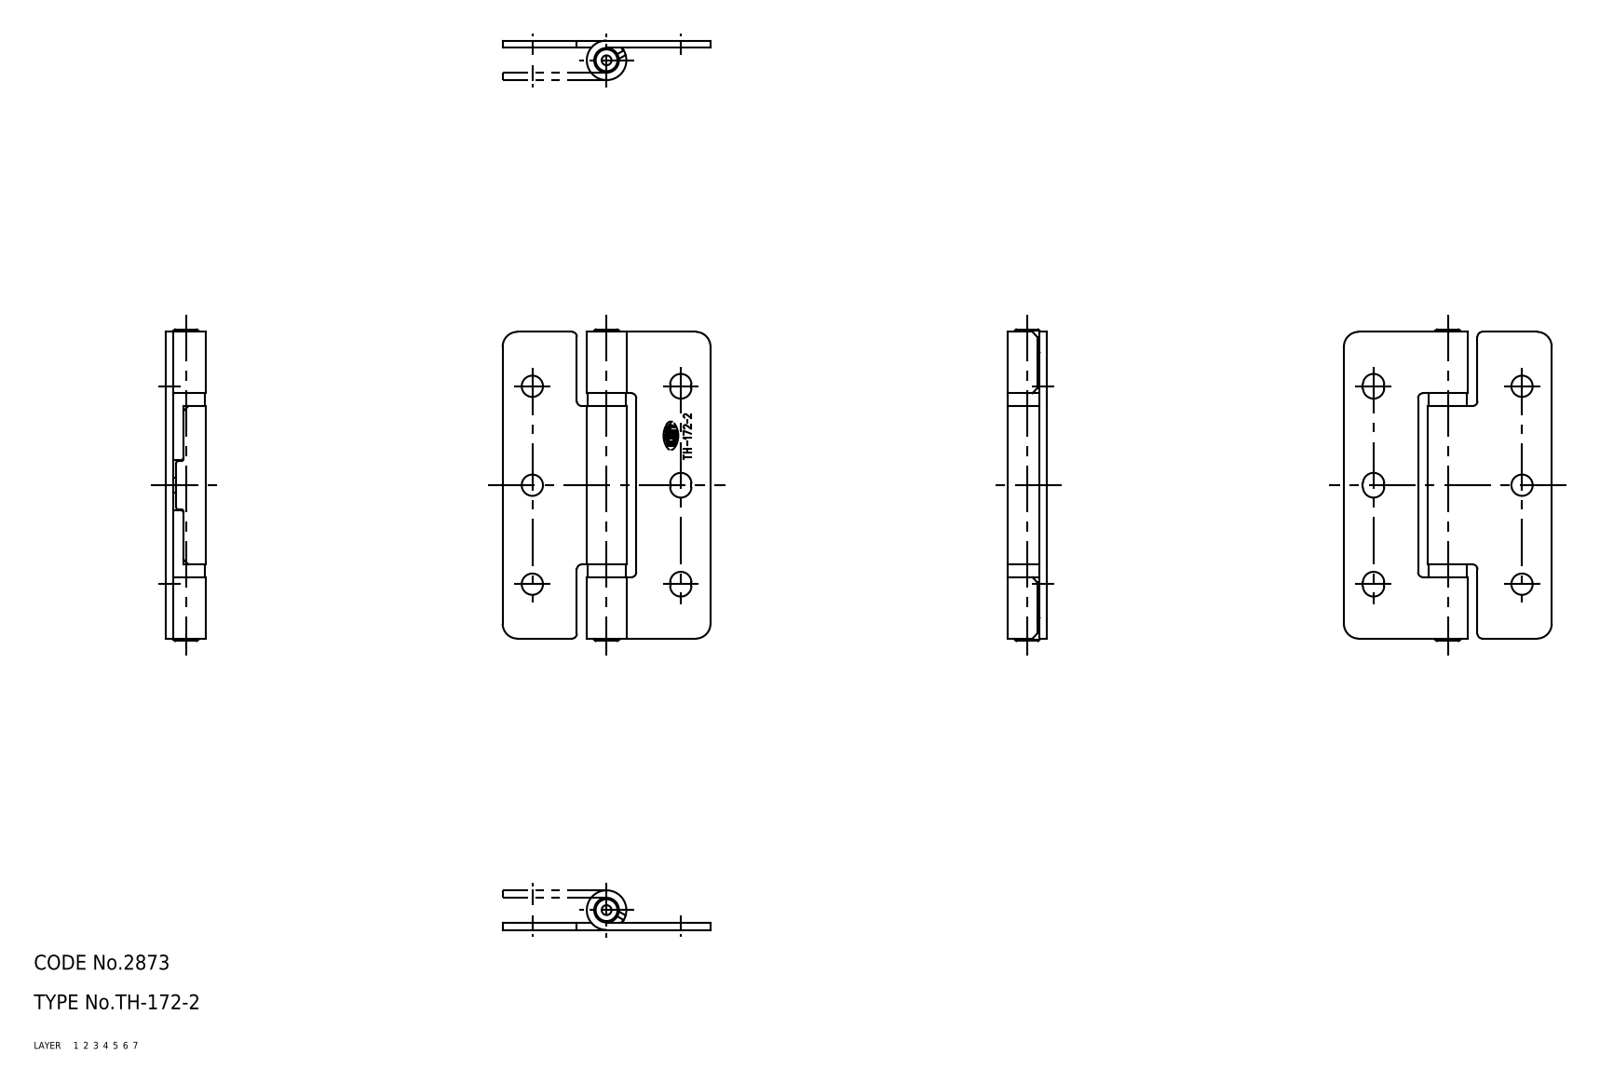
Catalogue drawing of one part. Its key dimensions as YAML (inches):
part_name: "67115473; 67115486; 67115499; 67115512 (+2 more)"
step_written_by: "CADfix (AUTOMOTIVE_DESIGN)"
units: inches
bodies: {solids: 6, faces: 118, planar: 0, cylindrical: 0, other: 118}
overall_size: [2.48, 1.654, 0.315]
volume: 0.356
surface_area: 13.79
